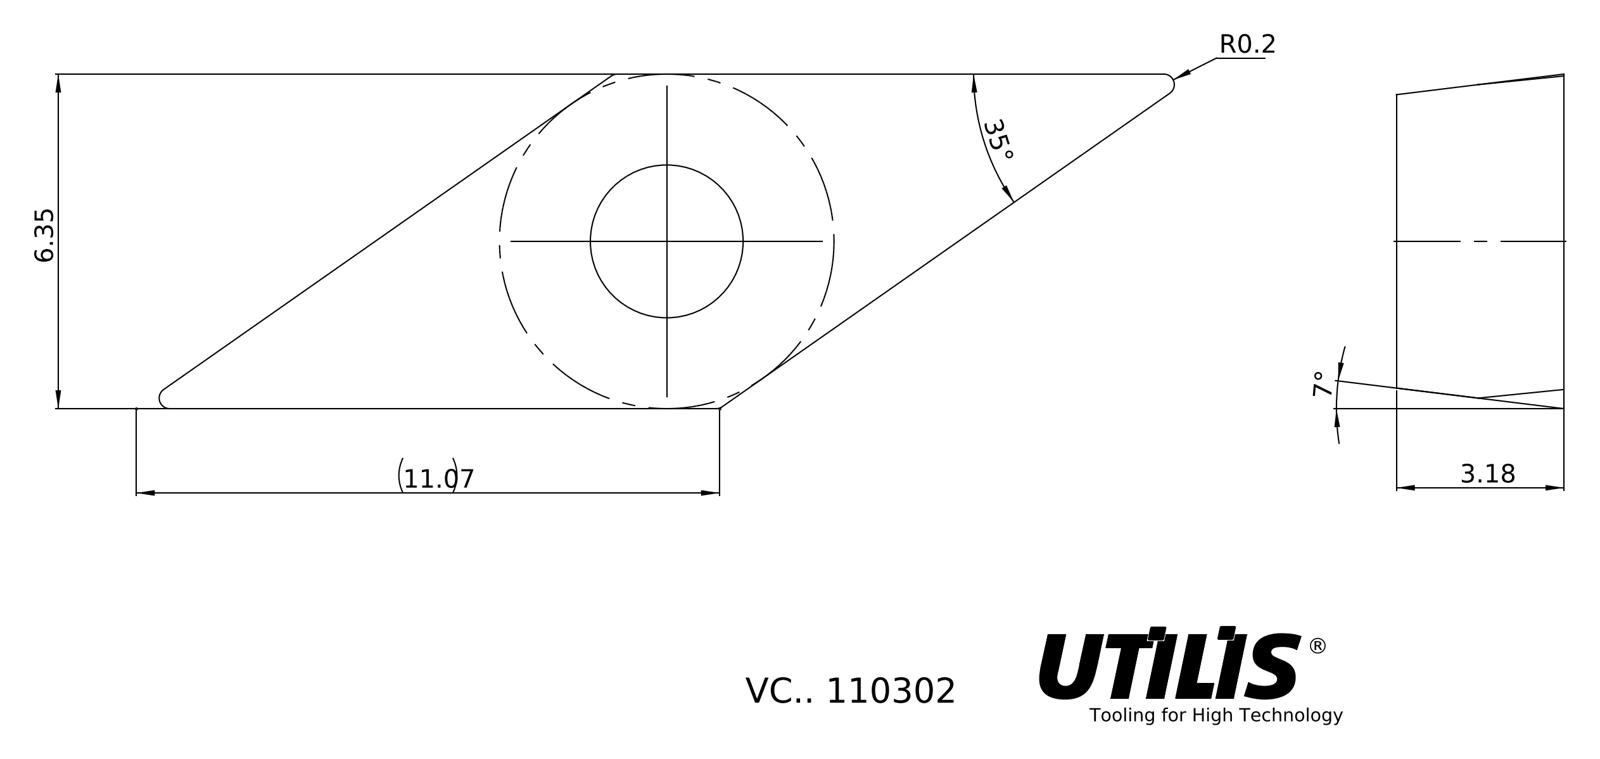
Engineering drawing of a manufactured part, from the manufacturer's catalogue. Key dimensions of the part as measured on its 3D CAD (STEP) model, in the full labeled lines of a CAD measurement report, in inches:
Part name (STEP PRODUCT): VC.. 110302
STEP written by: SolidWorks 2016 (AUTOMOTIVE_DESIGN)
Units: inches
Bodies: 1 solid, 13 faces (2 planar, 2 cylindrical, 9 other)
Overall size (bounding box): 0.759 × 0.25 × 0.125
Volume: 0.011 in³ · Surface area: 0.422 in²
Round holes (diameter × count): ⌀0.114 ×1
Main face-to-face distances: 0.125
